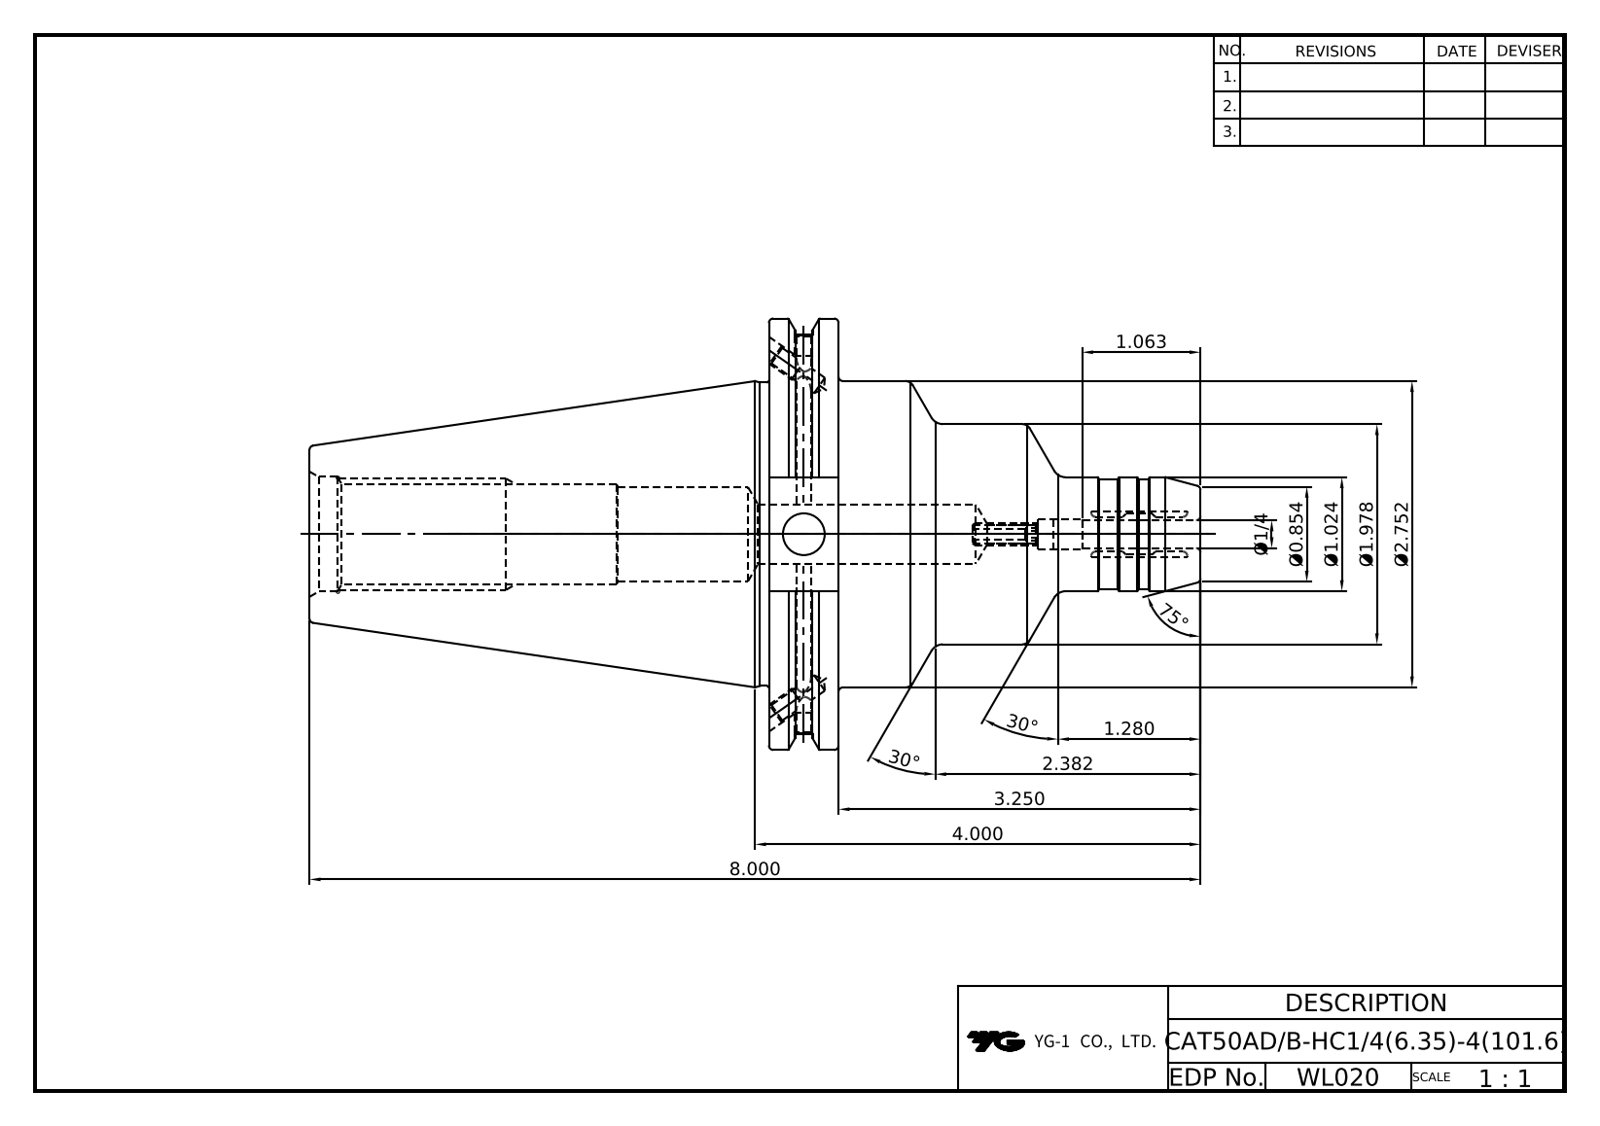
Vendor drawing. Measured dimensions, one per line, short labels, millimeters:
name: LO-CAT50ADB-HC6.35-101.6
written by: Autodesk Inventor 2022 (AUTOMOTIVE_DESIGN)
unit: mm
bodies: 1 solid, 112 faces (37 planar, 34 cylindrical, 41 other)
size: 203.2 × 98.42 × 94.69
volume: 463 295 mm³; area: 56 653 mm²
holes: 2× ⌀3.24, 2× ⌀4.13, 2× ⌀4.2, 2× ⌀5, 1× ⌀4.3, 1× ⌀6.35, 1× ⌀6.8, 1× ⌀9.53, 1× ⌀13.5, 1× ⌀20.5, 1× ⌀21.97, 1× ⌀26.2
bosses: 1× ⌀98.42, 1× ⌀91.29, 1× ⌀69.9, 1× ⌀69.25, 1× ⌀50.25, 1× ⌀26, 1× ⌀25
face distances: 15.88, 104.77, 120.65, 73.03, 203.2, 98.43, 82.55, 25.9, 110.82, 6.05
